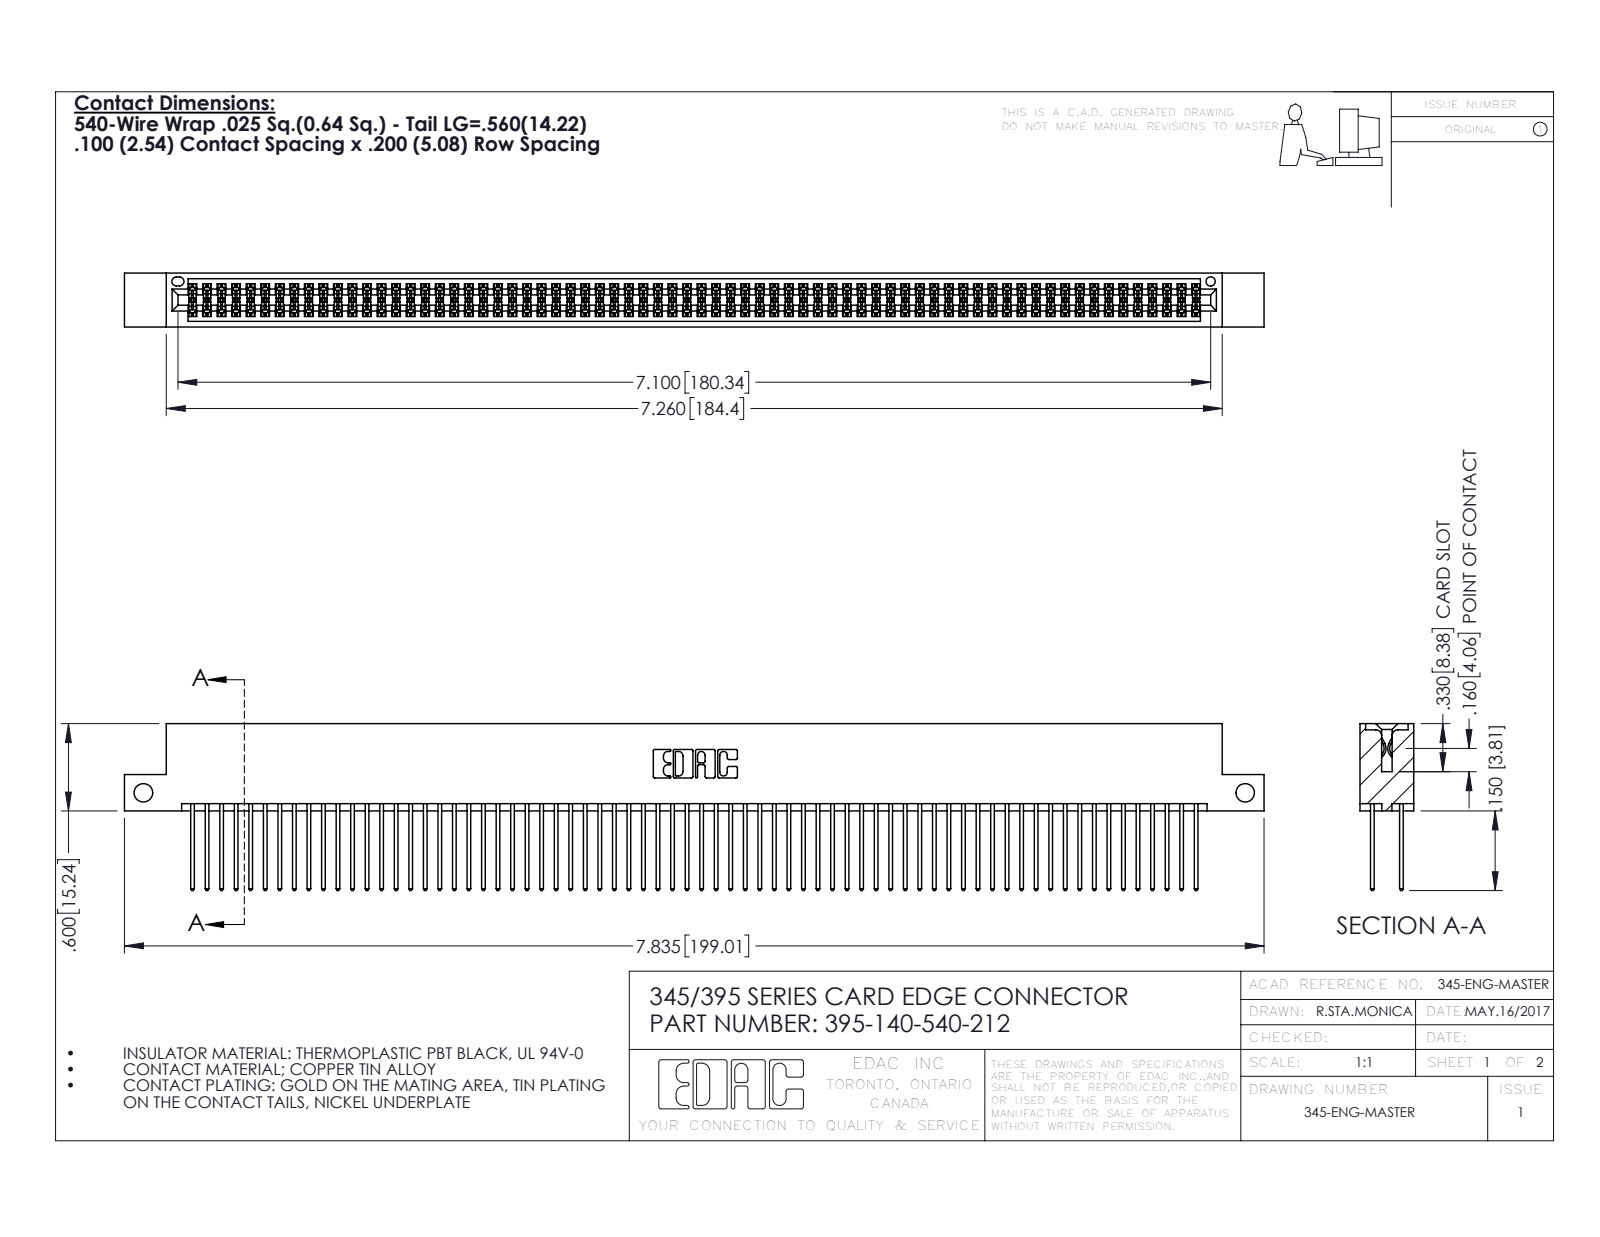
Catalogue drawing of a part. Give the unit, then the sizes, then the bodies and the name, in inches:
Units: inches
Overall size (bounding box): 7.835 × 1.147 × 0.37
Round holes (diameter × count): ⌀0.128 ×2, ⌀0.064 ×1
Partial cylindrical surfaces — rounded edges, fillets, slot ends (radius × count): R0.006 ×210, R0.01 ×140, R0.01 ×22, R0.007 ×6, R0.031 ×6, R0.026 ×3, R0.014 ×2, R0.019 ×2
Main face-to-face distances: 0.298, 0.072, 0.2, 0.098, 0.272, 0.025, 0.225, 0.37, 0.175, 0.149
Hole centre spacings: 7.575
Volume: 1.223 in³ · Surface area: 50.35 in²
Bodies: 141 solids, 7126 faces (4700 planar, 2426 cylindrical, 0 other)
Part name (STEP PRODUCT): 345 Part_Flush Mounting Lugs - Side Mount; 345-292-001_345-293-140; 395-140-540-212
STEP written by: SolidWorks 2016 (CONFIG_CONTROL_DESIGN)
